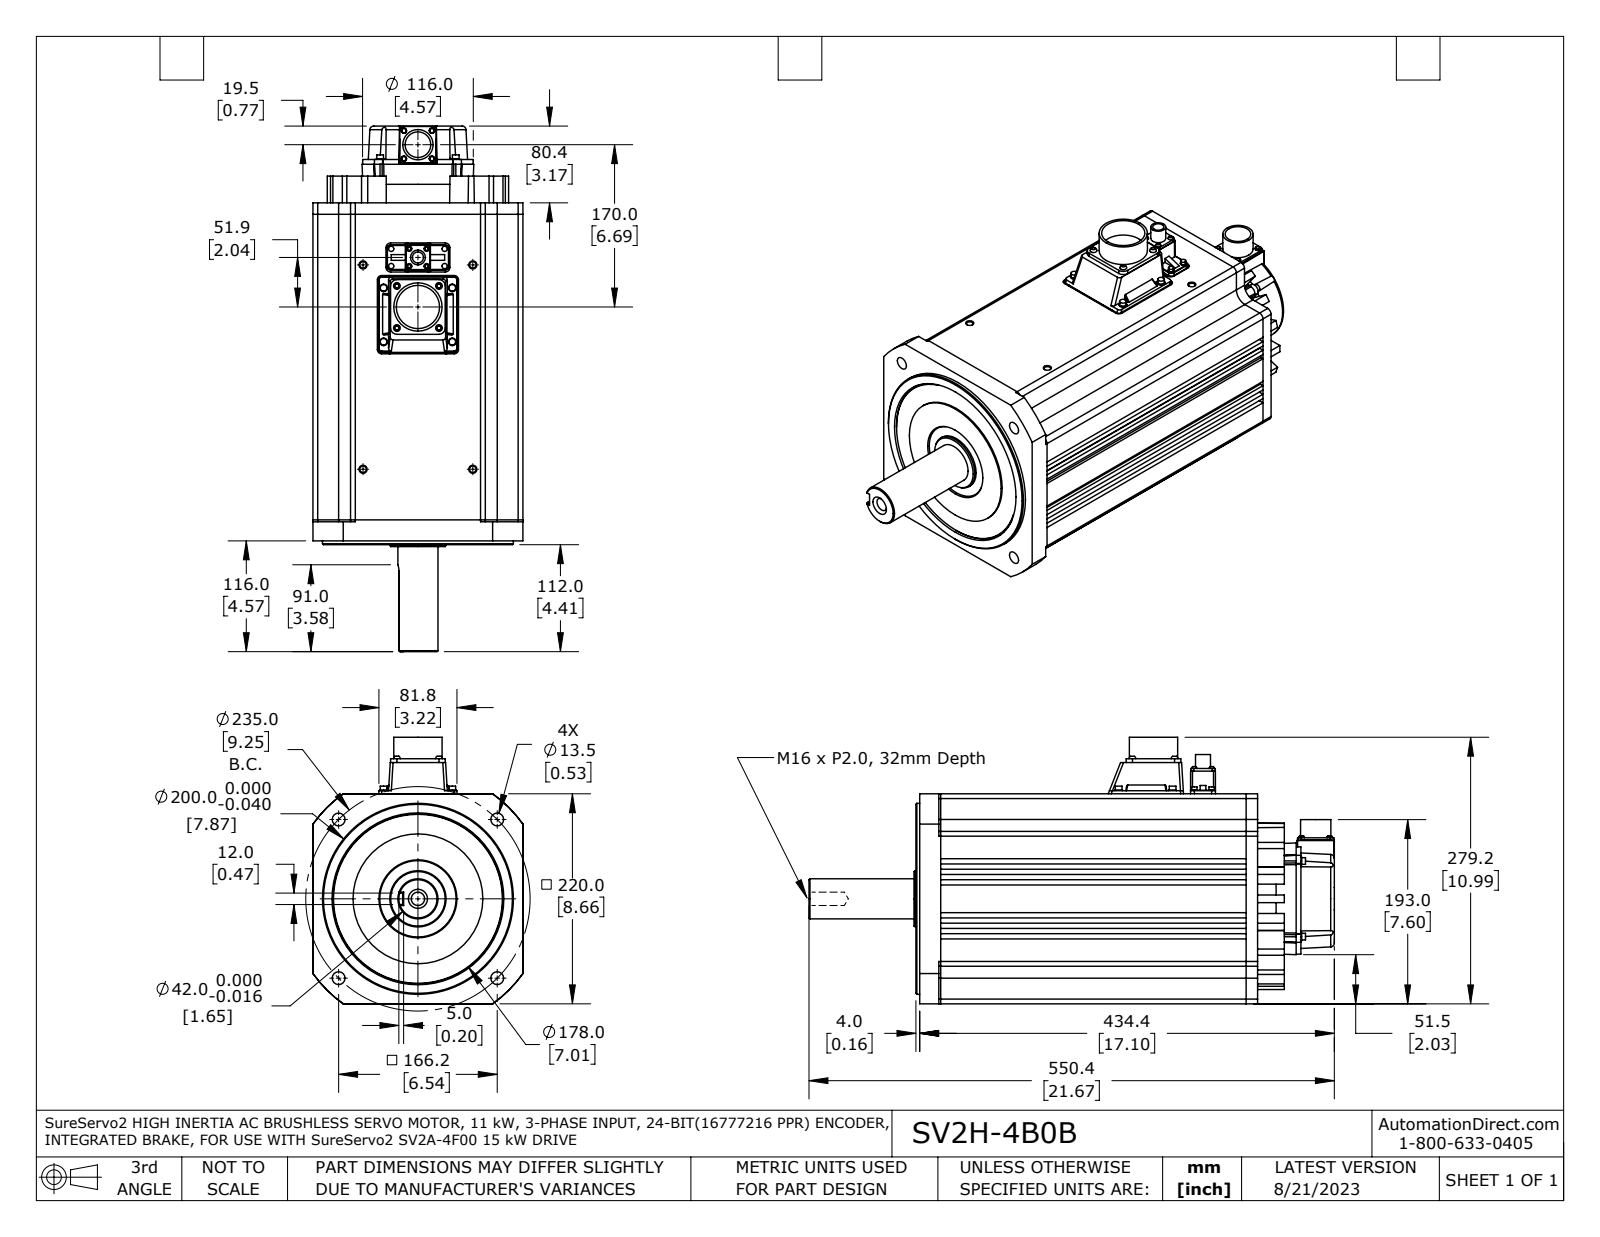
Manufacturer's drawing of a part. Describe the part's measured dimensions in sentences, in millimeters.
The part is named "SV2H-4B0B fxt r1". Its 3-D file was written by "SolidWorks 2021 (AUTOMOTIVE_DESIGN)". It is 1 solid with 824 faces: 403 planar, 260 cylindrical and 161 other. Overall it measures 550.5 by 279.2 by 220 millimeters. Its volume is 16 210 000 cubic millimeters and its surface area 591 200 square millimeters. Round holes: 4 of diameter 4.3, 4 of diameter 4.6, 4 of diameter 6.8, 4 of diameter 13.5, 1 of diameter 11.7, 1 of diameter 14, 1 of diameter 26.9, 1 of diameter 45.3, 1 of diameter 180. Round bosses or shafts: 8 of diameter 8, 8 of diameter 7, 4 of diameter 6, 4 of diameter 5.5, 4 of diameter 4, 1 of diameter 200, 1 of diameter 178, 1 of diameter 136. Partial cylindrical surfaces (rounded edges, fillets, slot ends): 31 of radius 0.5, 28 of radius 5, 20 of radius 3, 16 of radius 4, 4 of radius 1, 4 of radius 2, 4 of radius 4.5, 4 of radius 5.5. The main face-to-face distances are 220, 39.4, 180.6, 5.5, 11, 141.2, 62, 16.5, 56.5, 67.5. The hole center spacings are 117.5, 166.2, 32.3, 41.2, 48.1, 51.3, 56.5, 58.
